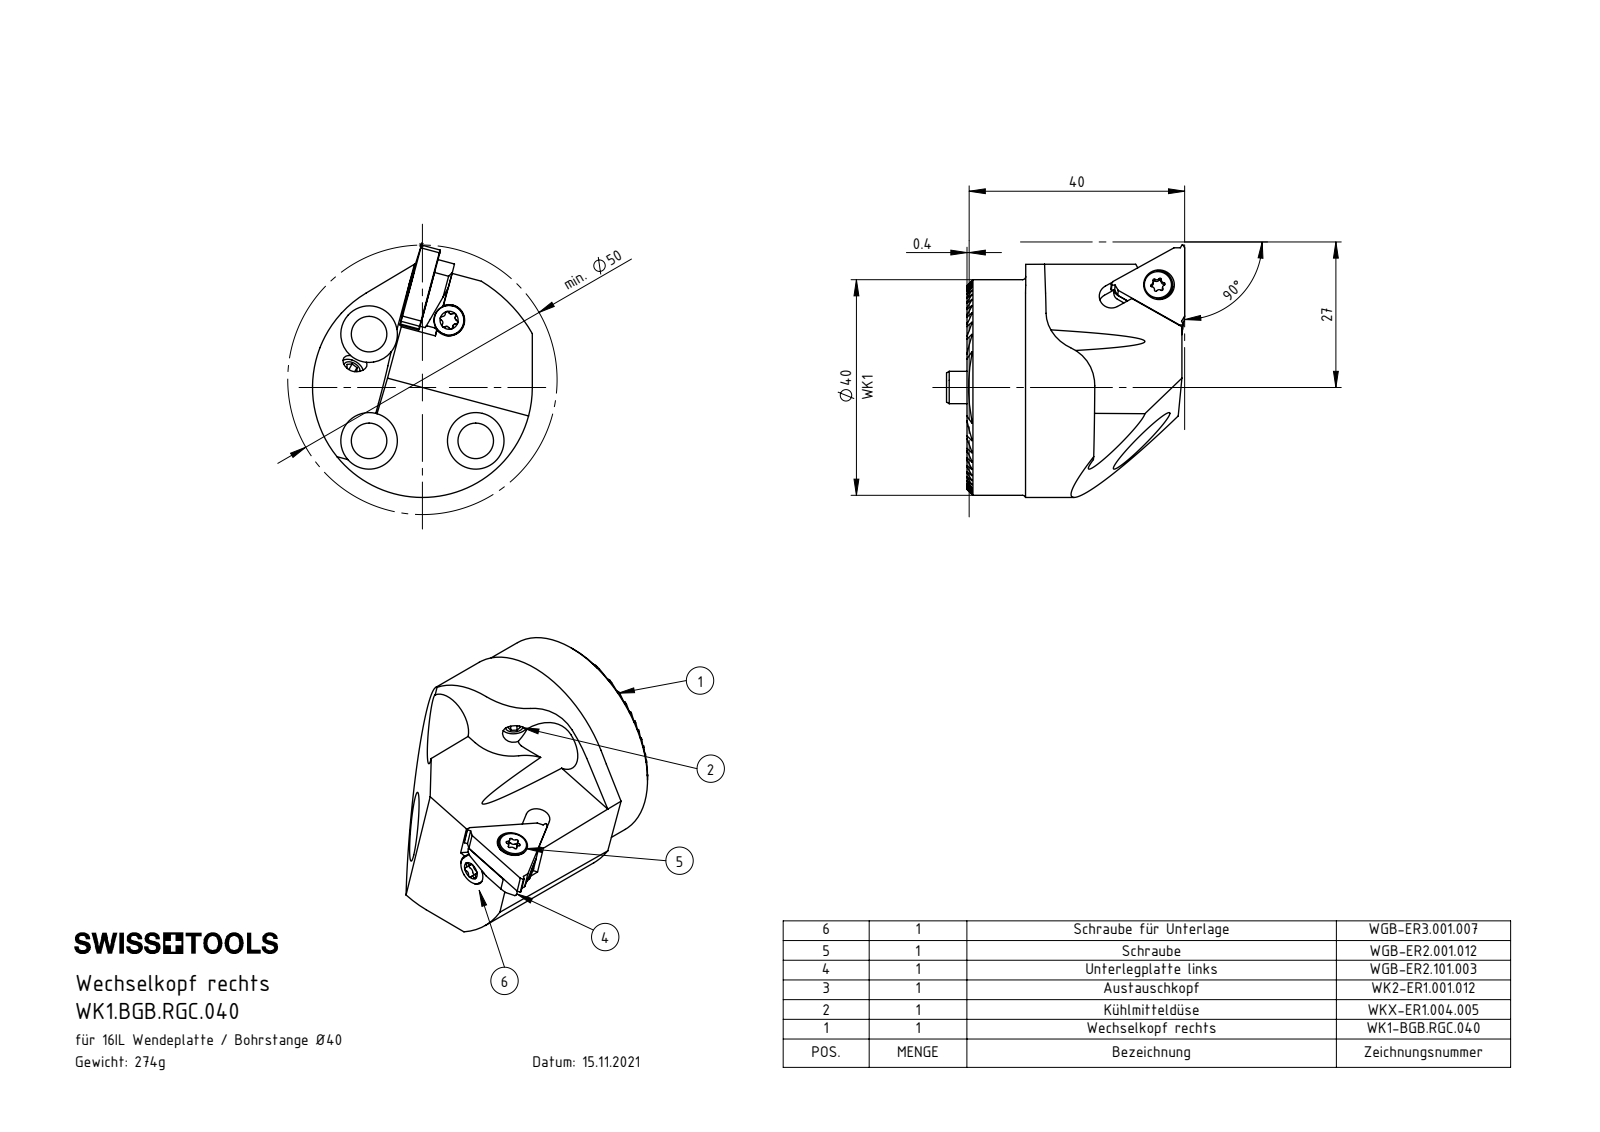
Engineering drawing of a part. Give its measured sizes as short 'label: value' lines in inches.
name: WK2-ER1.001.012_A_Fertigbearbeitung; WK1.BGB.RGC.040; LT16EL; WGB-ER2.001.012_A (+5 more)
written by: SolidWorks 2017 (AUTOMOTIVE_DESIGN)
unit: in
bodies: 9 solids, 466 faces (274 planar, 142 cylindrical, 50 other)
size: 1.867 × 1.743 × 1.654
volume: 2.187 in³; area: 19.34 in²
holes: 3× ⌀0.26, 3× ⌀0.413, 2× ⌀0.102, 2× ⌀0.13, 2× ⌀0.157, 1× ⌀0.067, 1× ⌀0.118, 1× ⌀0.158, 1× ⌀0.165, 1× ⌀0.177, 1× ⌀0.472
bosses: 2× ⌀0.217, 2× ⌀0.157, 1× ⌀1.575, 1× ⌀0.236, 1× ⌀0.125, 1× ⌀0.118, 1× ⌀0.109
rounds: 32× R0.005, 6× R0.009, 6× R0.013, 6× R0.022, 6× R0.022, 2× R0.004, 2× R0.01, 2× R0.394
face distances: 0.17, 0.043, 0.128, 0.341, 0.213, 0.298, 0.106, 0.085, 0.085, 0.383
hole spacings: 0.551, 0.78, 1.102
